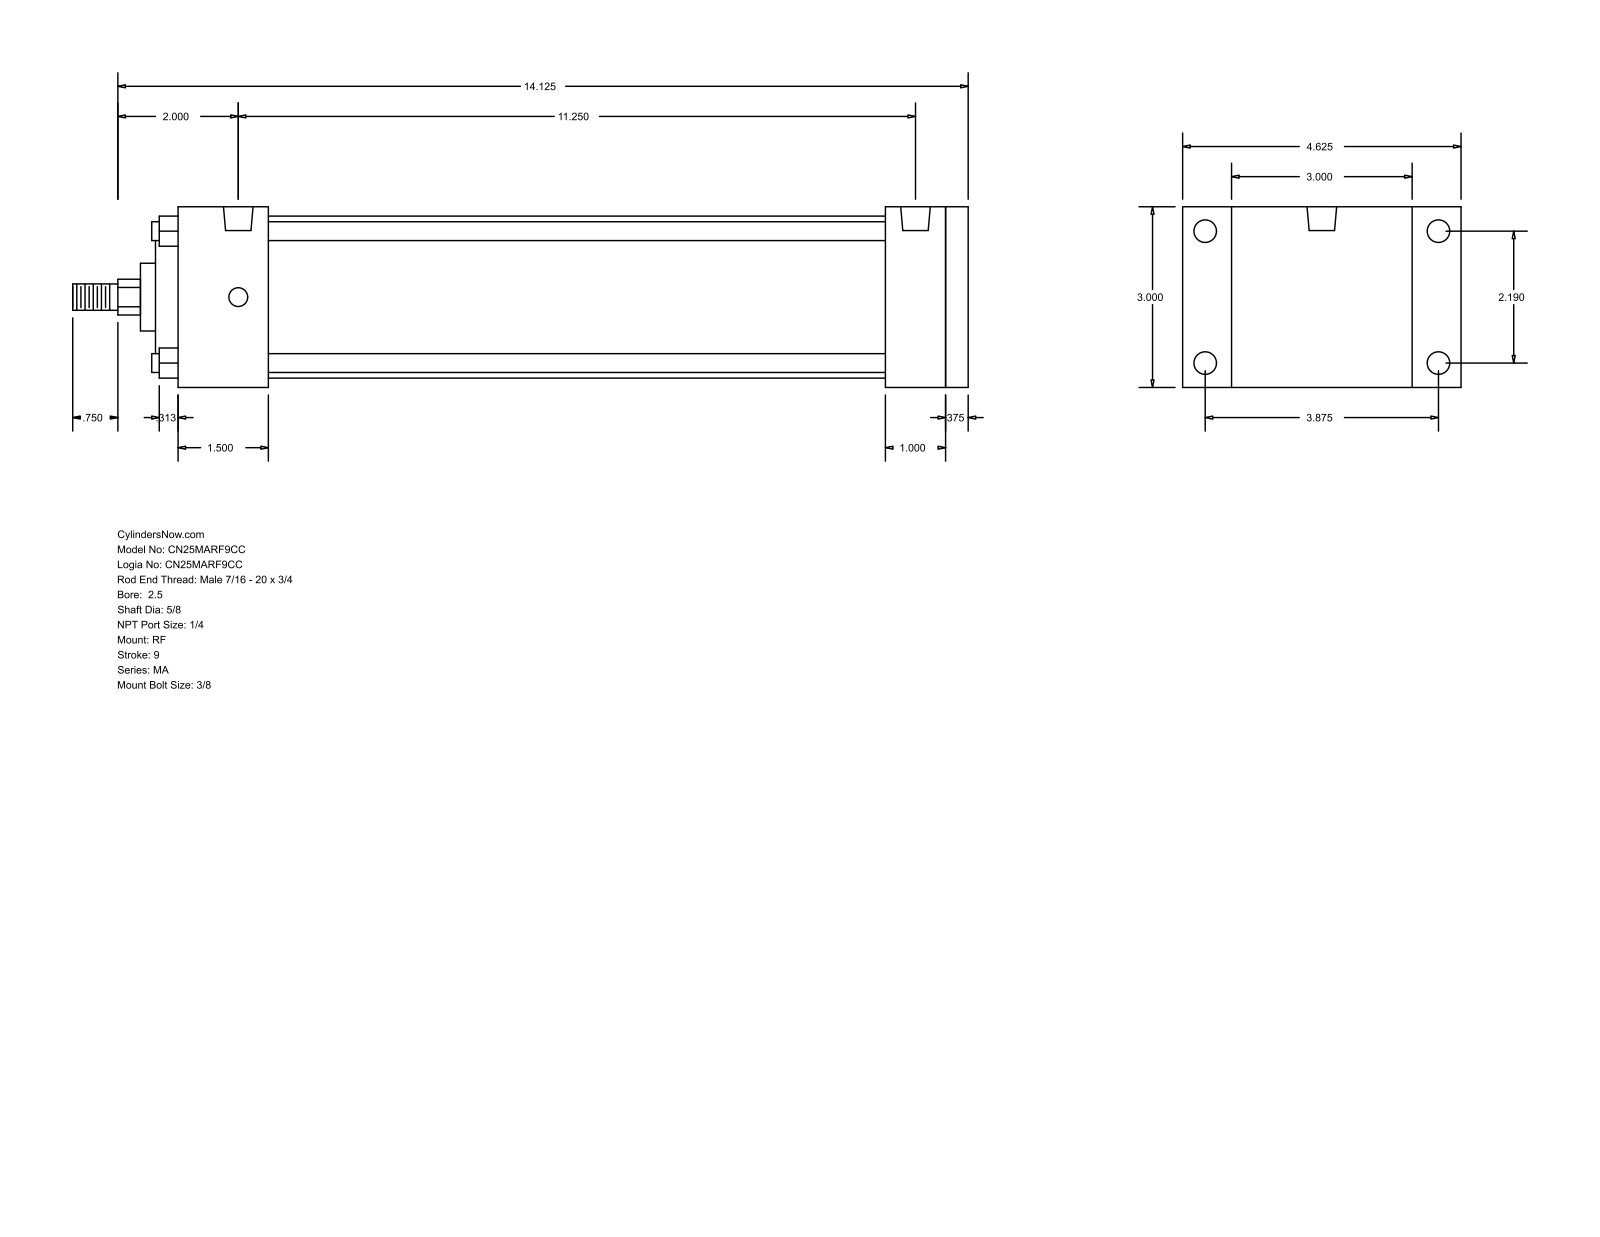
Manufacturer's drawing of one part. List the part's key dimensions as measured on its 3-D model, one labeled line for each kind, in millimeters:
Part name (STEP PRODUCT): MA_RF__0250_0.625
STEP written by: GSSL Pune (CONFIG_CONTROL_DESIGN)
Units: millimetres
Bodies: 0 solids, 94 faces (65 planar, 29 cylindrical, 0 other)
Overall size (bounding box): 377.82 × 117.47 × 76.2
Round holes (diameter × count): ⌀7.94 ×4, ⌀9.53 ×4, ⌀12.49 ×2
Round bosses / shafts (diameter × count): ⌀7.94 ×4, ⌀68.33 ×1, ⌀50.8 ×1, ⌀28.57 ×1, ⌀15.88 ×1, ⌀11.11 ×1
Partial cylindrical surfaces — rounded edges, fillets, slot ends (radius × count): R7.54 ×1
Main face-to-face distances: 76.2, 333.37, 9.52, 323.85, 25.4, 38.1, 298.45, 260.35, 285.75, 295.27
Hole centre spacings: 55.62, 98.42, 113.05, 285.75
